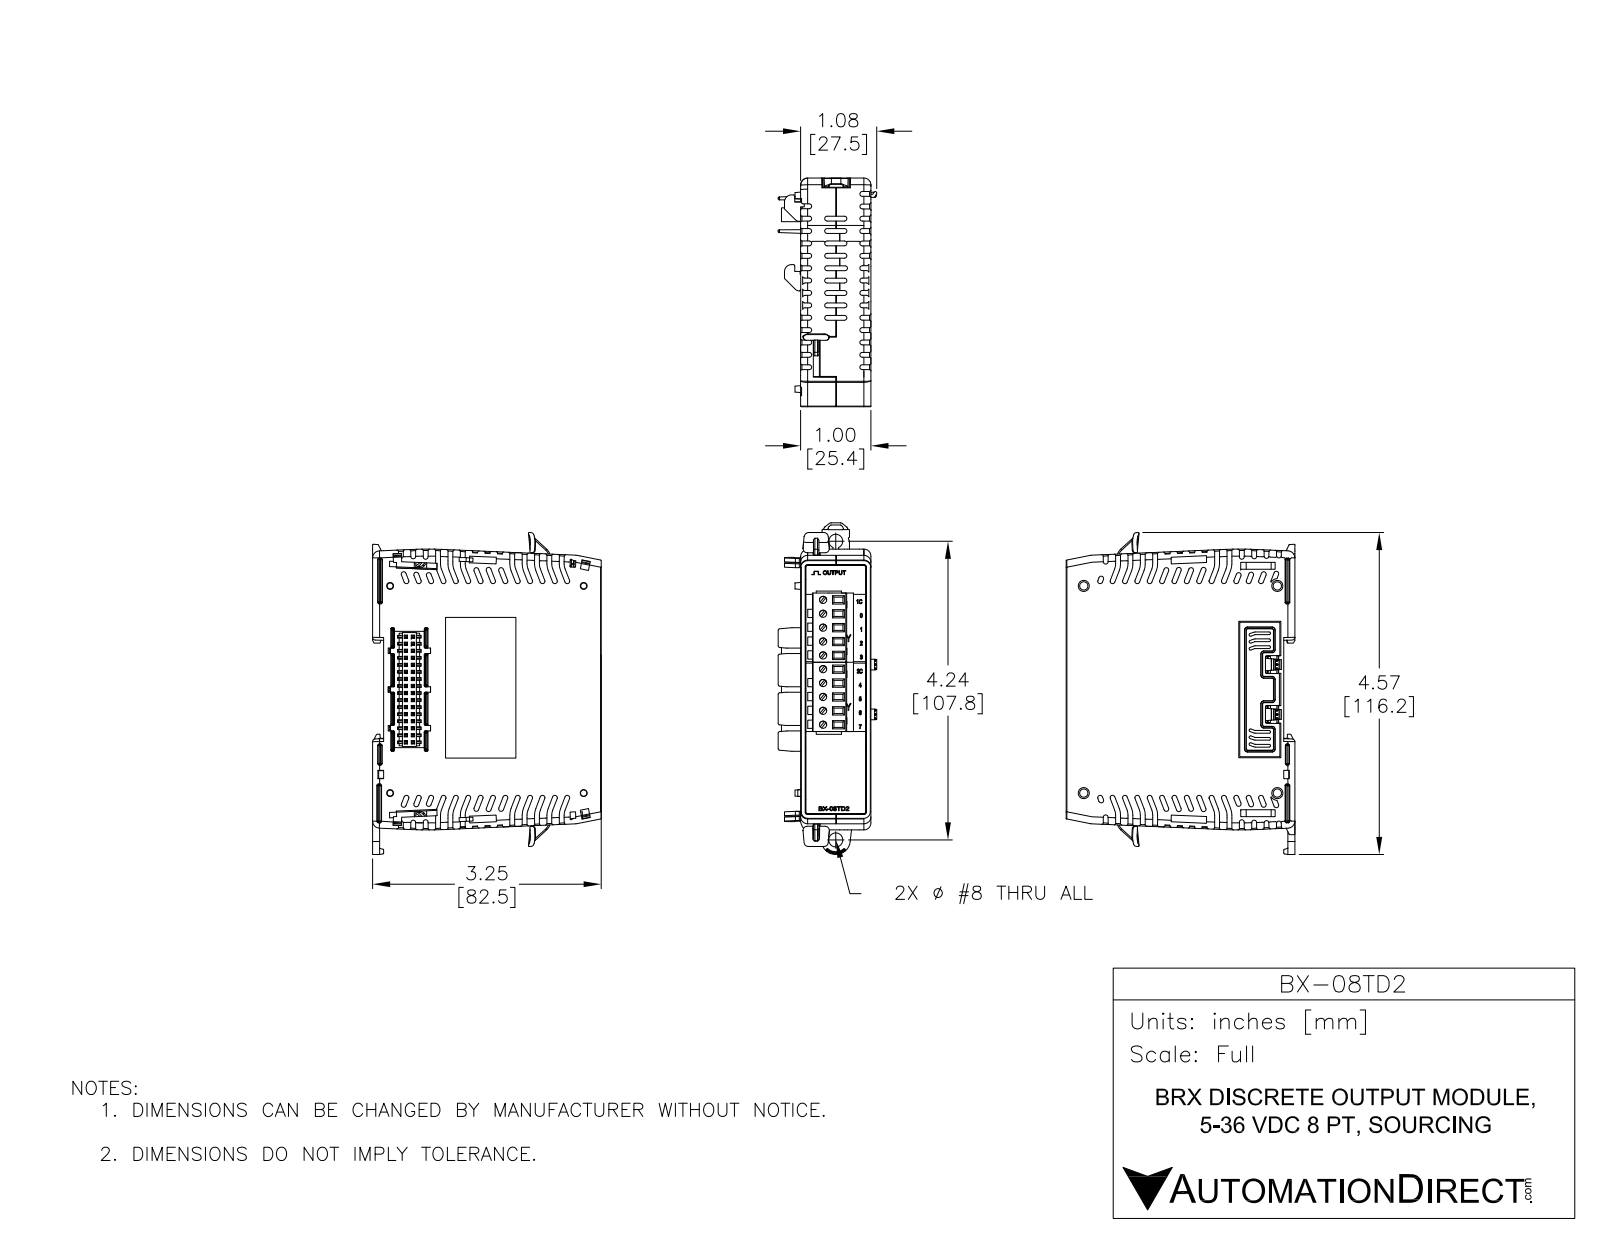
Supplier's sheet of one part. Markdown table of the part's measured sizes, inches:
| quantity | value |
| --- | --- |
| part name | BX-08TD2 |
| STEP written by | SolidWorks 2017 (AUTOMOTIVE_DESIGN) |
| units | inches |
| bodies | 22 solids, 3587 faces (2540 planar, 563 cylindrical, 484 other) |
| overall size | 4.586 × 3.311 × 1.402 |
| volume | 11.59 in³ |
| surface area | 72.76 in² |
| round holes (diameter × count) | 0.047 × 2, 0.065 × 2, 0.118 × 2, 0.118 × 2, 0.199 × 1 |
| round bosses / shafts (diameter × count) | 0.062 × 2, 0.059 × 2 |
| partial cylindrical surfaces (radius × count) | 0.005 × 102, 0.01 × 47, 0.02 × 34, 0.005 × 24, 0.008 × 21, 0.117 × 14, 0.039 × 13, 0.01 × 12 |
| main face-to-face distances | 1, 3.211, 3.22, 0.475, 0.1, 0.157, 3.053, 3.063, 0.787, 0.63 |
| hole center spacings | 0.1, 0.824, 0.919, 1.3, 2.093, 2.193, 2.585, 2.617 |
